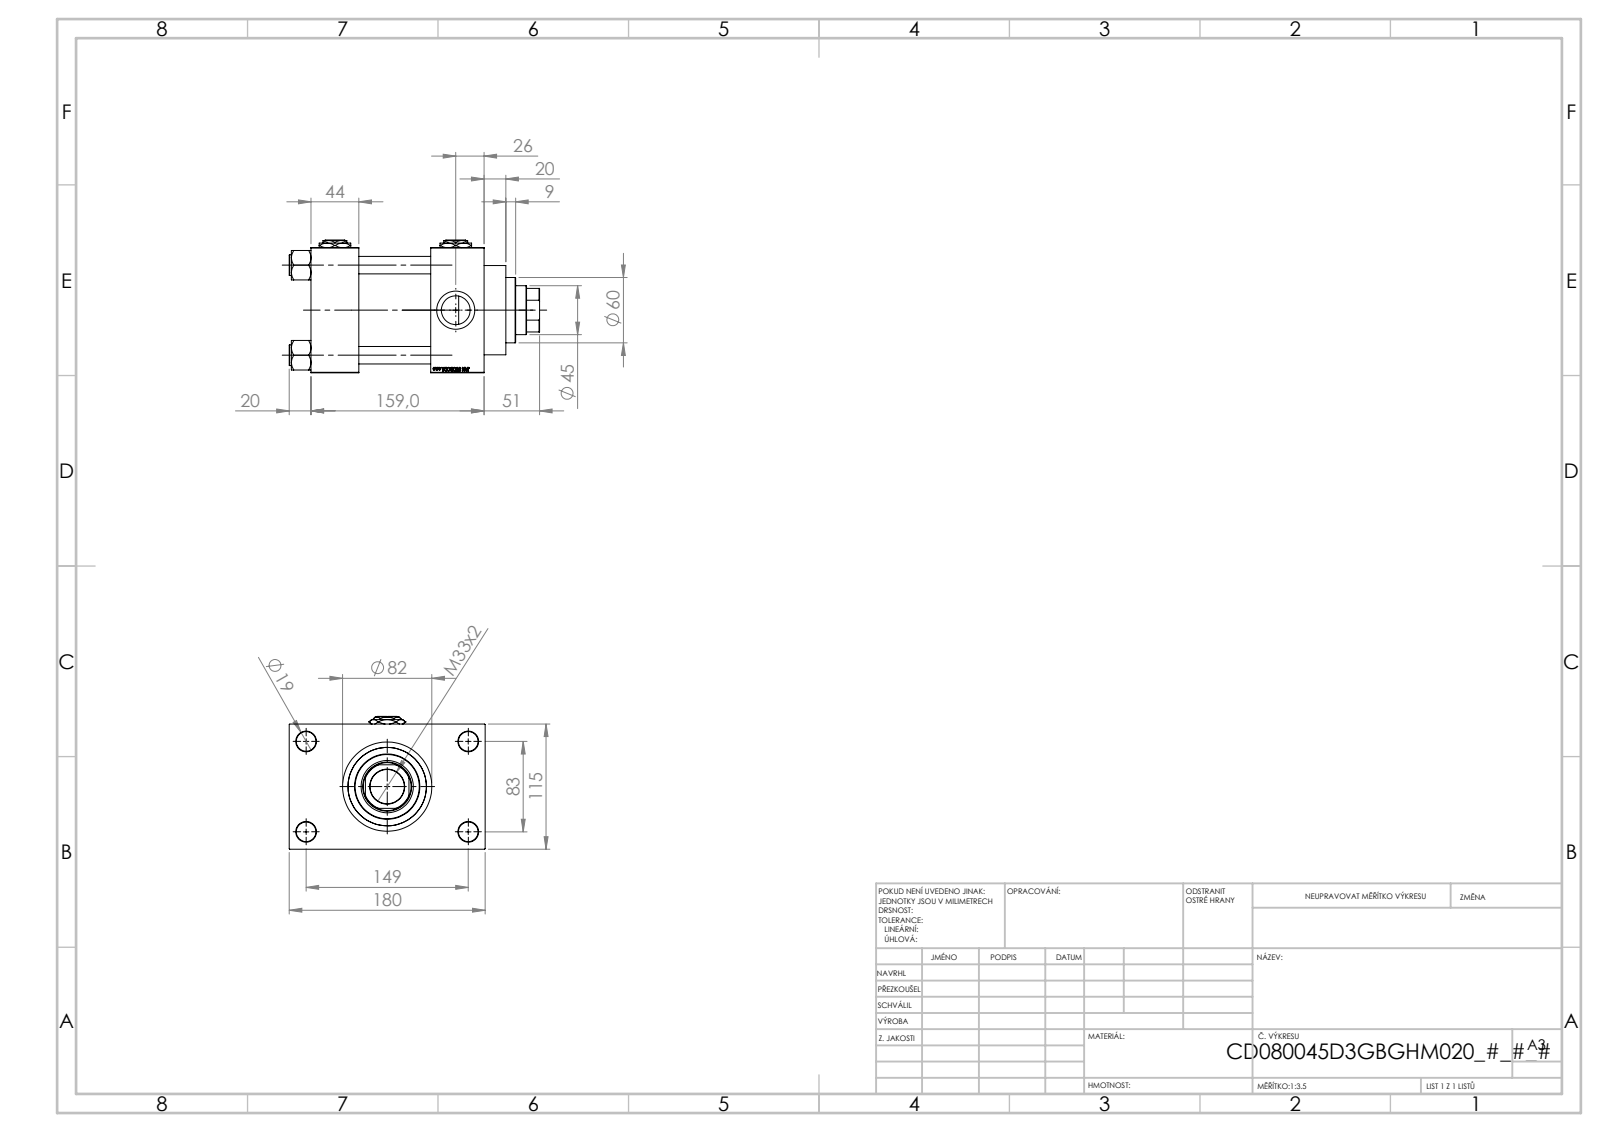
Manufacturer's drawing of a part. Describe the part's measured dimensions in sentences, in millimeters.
The part is named "Zatka_pro_OIL_PORT; V215CD_NUT_M5_D; V215CD_VC_A; V215CD_D_TYCINKA (+2 more)". Its 3-D file was written by "SolidWorks 2019 (CONFIG_CONTROL_DESIGN)". It is 13 solids with 1252 faces: 593 planar, 99 cylindrical and 560 other. Overall it measures 230 by 180 by 122 millimeters. Its volume is 1 991 000 cubic millimeters and its surface area 309 018 square millimeters. Round holes: 4 of diameter 16, 4 of diameter 18, 4 of diameter 26.44, 4 of diameter 35, 3 of diameter 7, 1 of diameter 31.5, 1 of diameter 45, 1 of diameter 48, 1 of diameter 61, 1 of diameter 72, 1 of diameter 80. Round bosses or shafts: 4 of diameter 19, 1 of diameter 86, 1 of diameter 82, 1 of diameter 60. Partial cylindrical surfaces (rounded edges, fillets, slot ends): 1 of radius 22. The main face-to-face distances are 115, 110, 66, 49, 44, 159, 147.5, 32.5, 20, 69. The hole center spacings are 33.15, 58.48, 82.7, 85.28, 89.24, 115.85, 142.43, 83.
